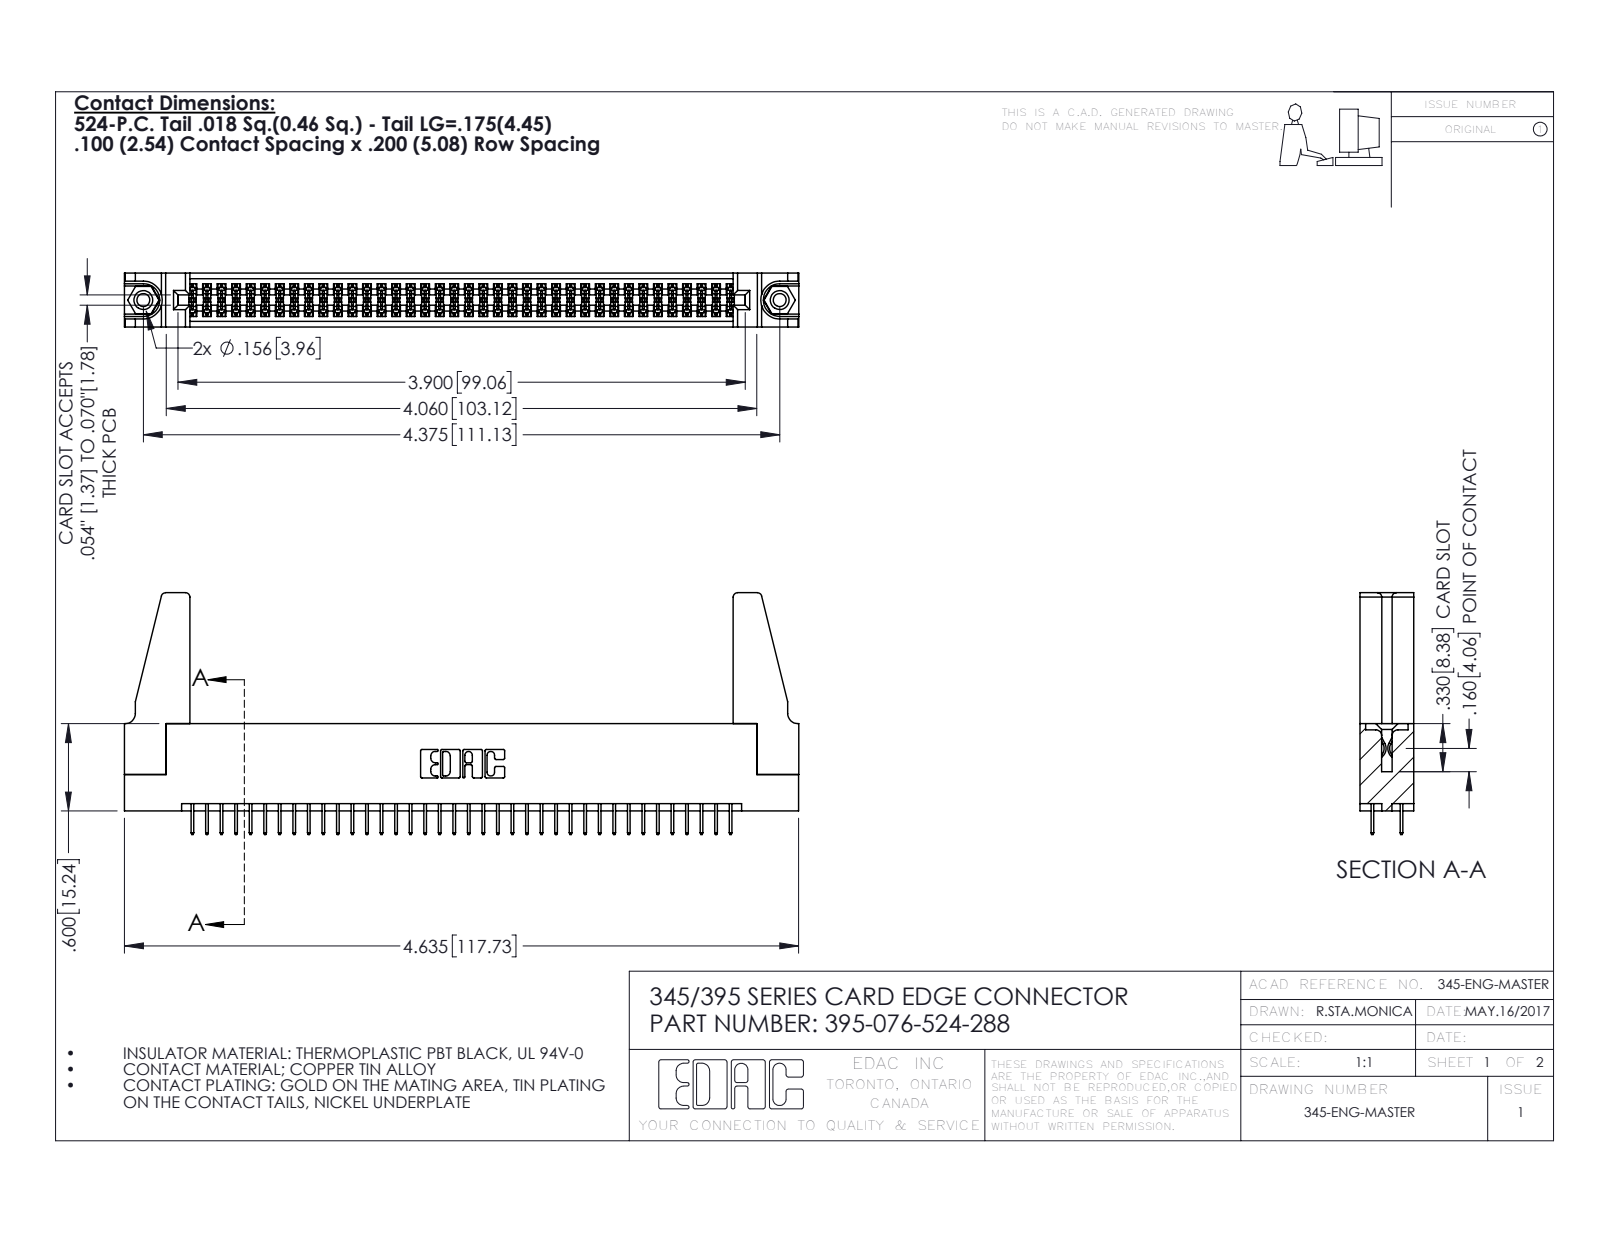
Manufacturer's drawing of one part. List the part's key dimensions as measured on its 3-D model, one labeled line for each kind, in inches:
Part name (STEP PRODUCT): 345-250-001_345-250-001-102; 345 Part_Flush Mounting Lugs - 0.156 Dia-TH; 345-292-001_345-293-124; 395-076-524-288 (+1 more)
STEP written by: SolidWorks 2016 (CONFIG_CONTROL_DESIGN)
Units: inches
Bodies: 81 solids, 4354 faces (3116 planar, 1222 cylindrical, 16 other)
Overall size (bounding box): 4.636 × 1.662 × 0.37
Volume: 0.887 in³ · Surface area: 30.11 in²
Round holes (diameter × count): ⌀0.089 ×2, ⌀0.125 ×2, ⌀0.156 ×2, ⌀0.064 ×1
Round bosses / shafts (diameter × count): ⌀0.155 ×2
Partial cylindrical surfaces — rounded edges, fillets, slot ends (radius × count): R0.006 ×114, R0.01 ×22, R0.03 ×8, R0.007 ×6, R0.031 ×6, R0.026 ×3, R0.014 ×2, R0.019 ×2
Main face-to-face distances: 0.072, 0.298, 0.37, 0.2, 0.098, 0.272, 0.025, 0.225, 0.072, 0.175
Hole centre spacings: 0.27, 4.139, 4.375
